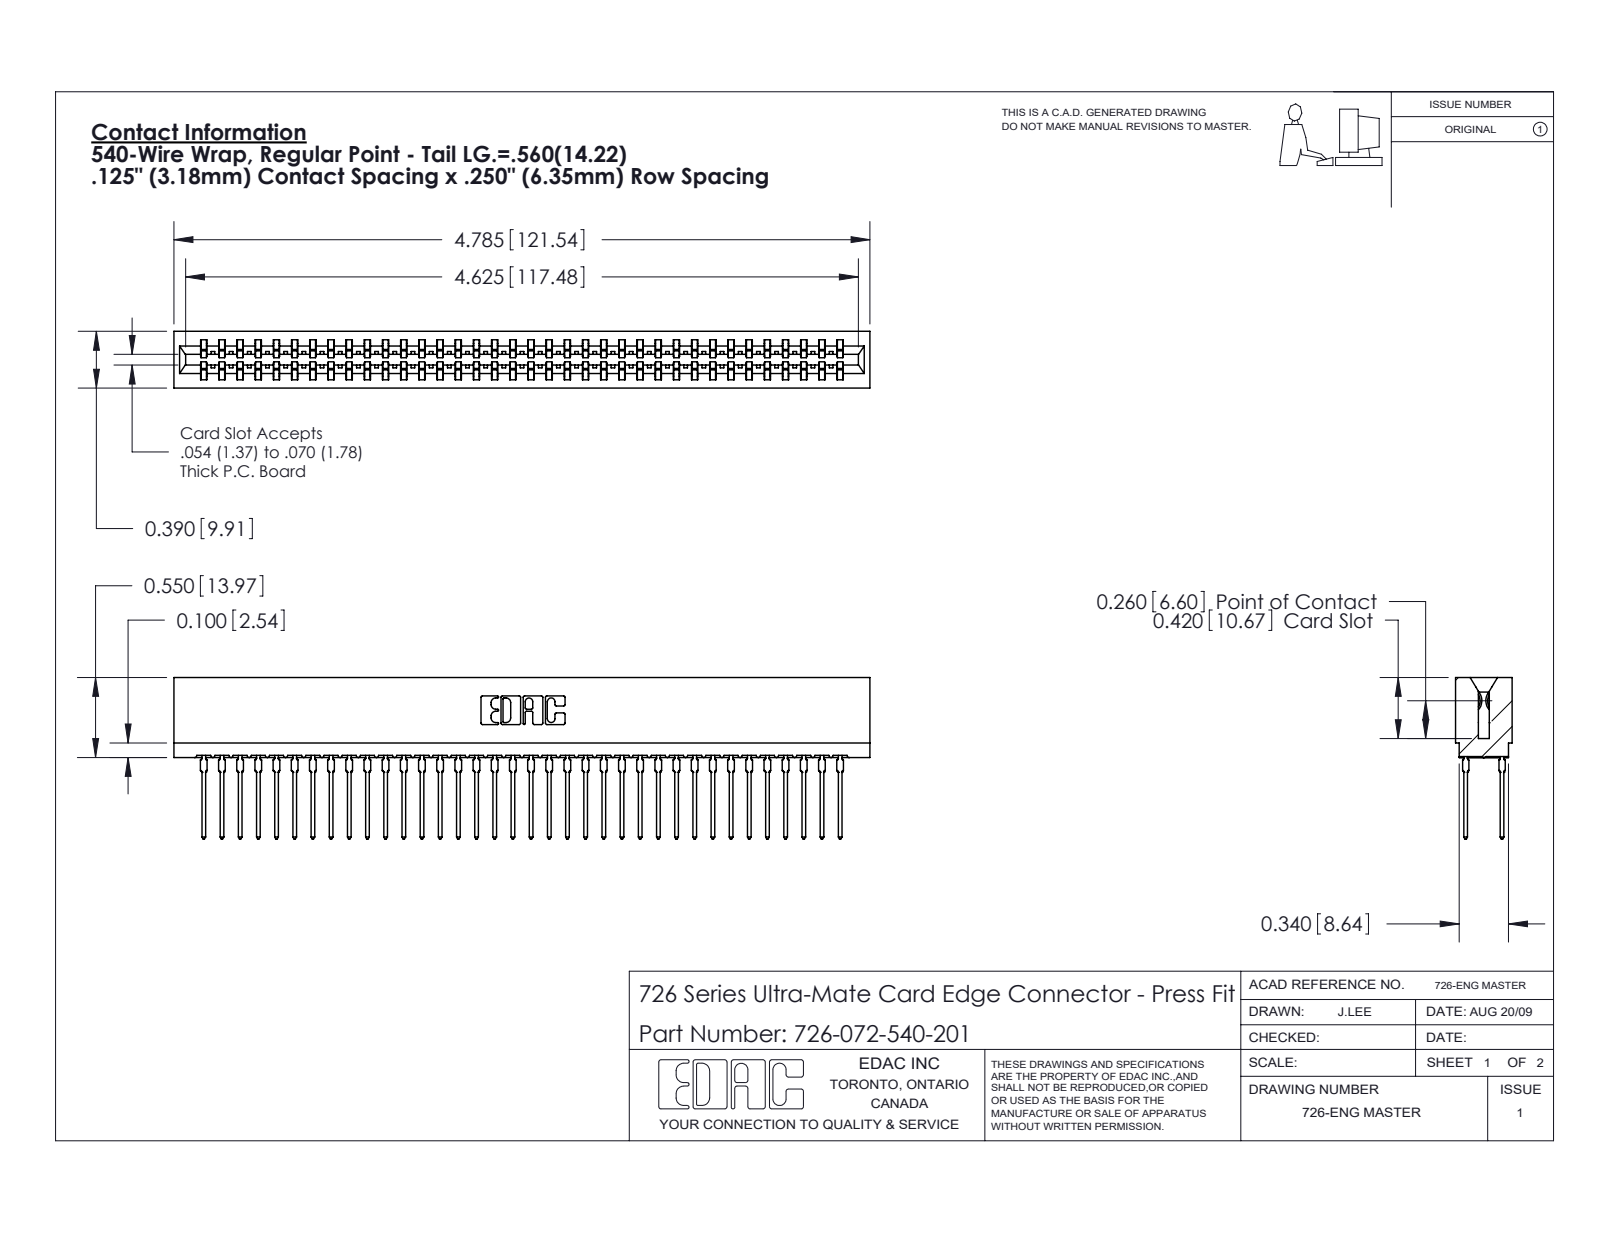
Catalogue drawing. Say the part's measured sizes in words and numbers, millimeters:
The part is named "746-292-001_540; 726 Part_.515 Slot Depth - 01; 726-072-540-201". Its 3-D file was written by "SolidWorks 2020 (CONFIG_CONTROL_DESIGN)". It is 73 solids with 6541 faces: 3367 planar, 1302 cylindrical and 1872 other. Overall it measures 121.5 by 28.2 by 9.9 millimeters. Its volume is 11 400 cubic millimeters and its surface area 19 960 square millimeters. Partial cylindrical surfaces (rounded edges, fillets, slot ends): 144 of radius 0.5, 37 of radius 0.4, 22 of radius 0.3, 8 of radius 0.1, 8 of radius 0.3, 6 of radius 0.2, 6 of radius 0.8, 3 of radius 0.7. The main face-to-face distances are 1.4, 8.5, 0.6, 6.4, 7.8, 9.9, 2.1, 7, 12.7, 9.3.
